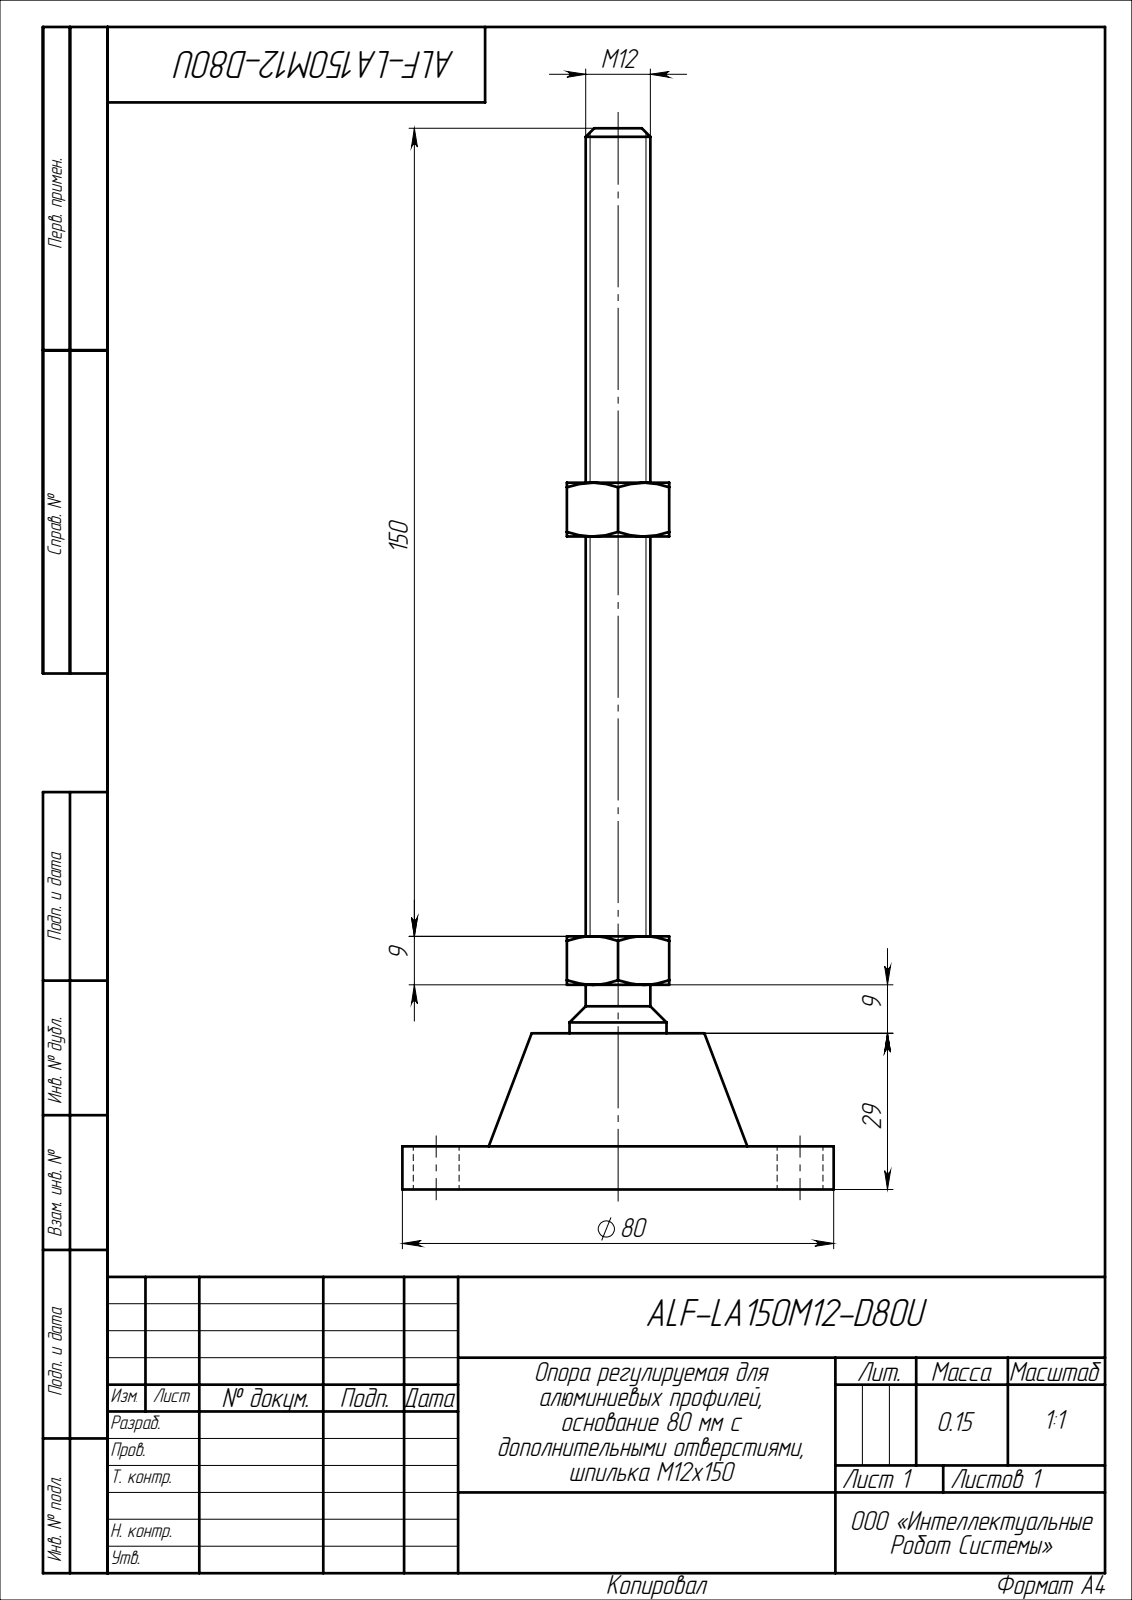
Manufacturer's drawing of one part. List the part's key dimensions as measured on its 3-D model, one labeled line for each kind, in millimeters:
Part name (STEP PRODUCT): ALF-LA150M12-D80U
STEP written by: SolidWorks 2022 (CONFIG_CONTROL_DESIGN)
Units: millimetres
Bodies: 1 solid, 64 faces (20 planar, 14 cylindrical, 30 other)
Overall size (bounding box): 197 × 80 × 80
Volume: 89 244 mm³ · Surface area: 21 634 mm²
Round holes (diameter × count): ⌀8.5 ×2
Round bosses / shafts (diameter × count): ⌀80 ×1, ⌀18 ×1, ⌀12 ×1
Main face-to-face distances: 8, 19, 29, 21, 9, 131.2, 123.2, 102.2, 38, 30
Hole centre spacings: 67.5
